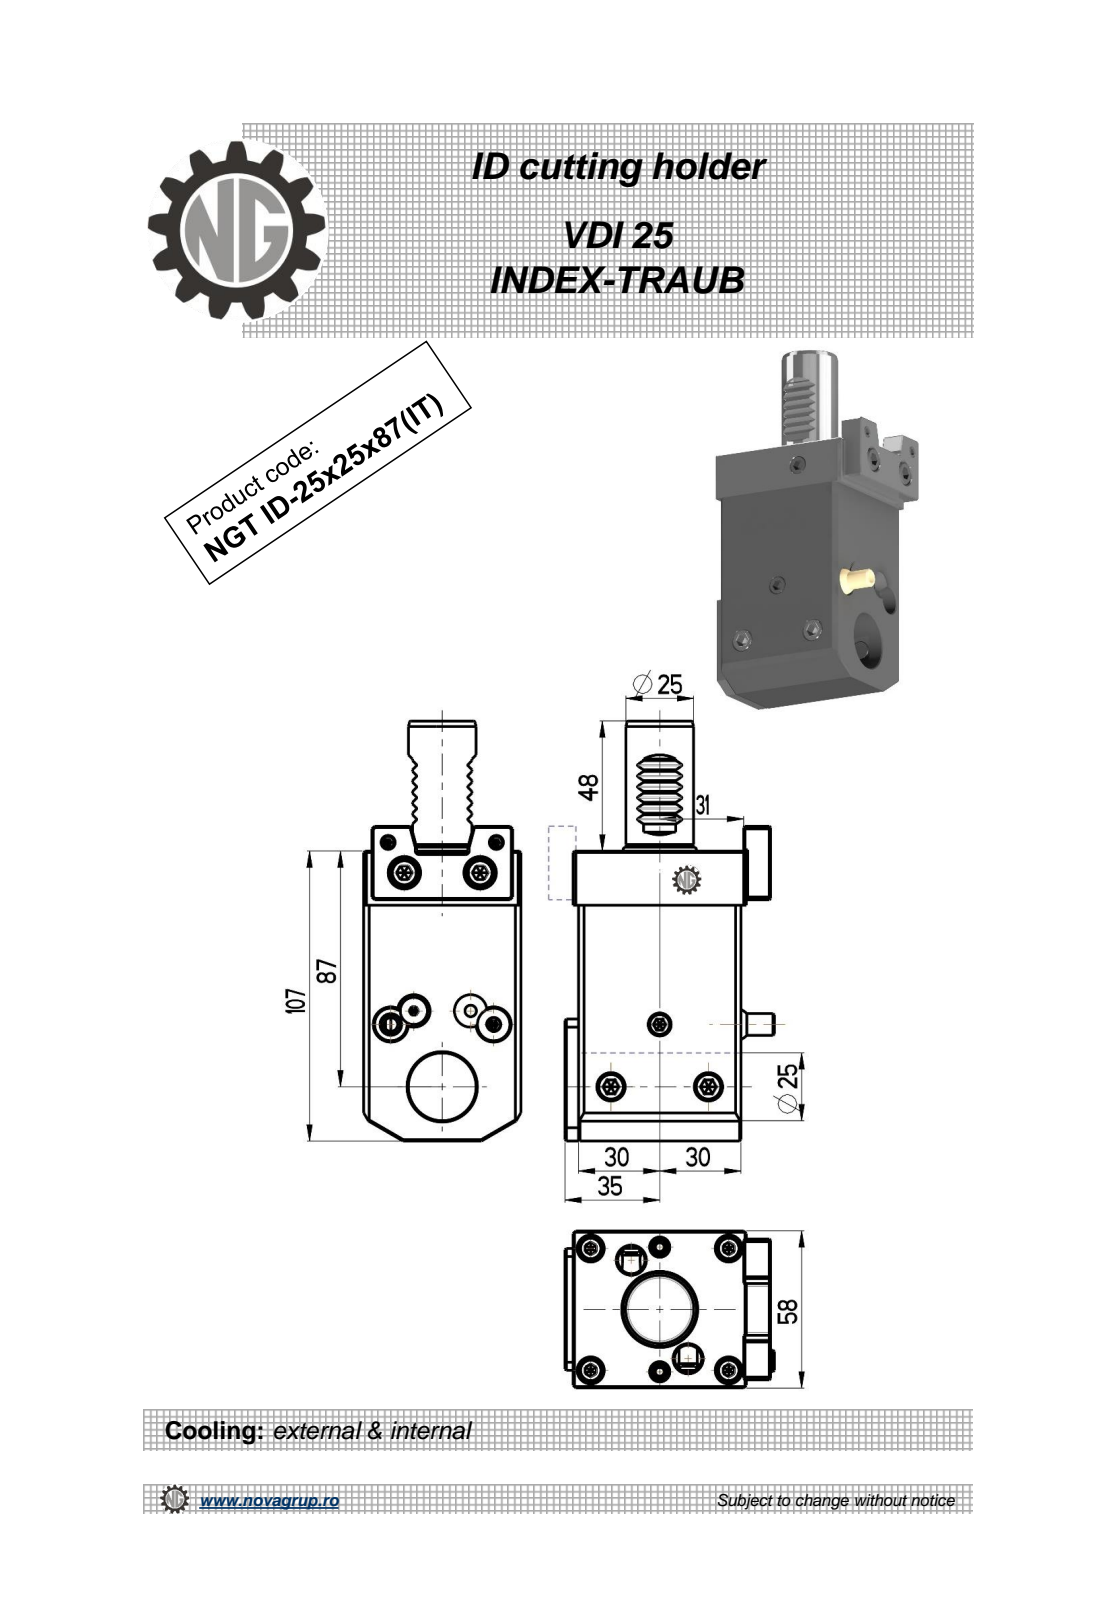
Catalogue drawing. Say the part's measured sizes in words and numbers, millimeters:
The part is named "NGT_ID_25_25_87_IT". Its 3-D file was written by "PRO/ENGINEER BY PARAMETRIC TECHNOLOGY CORPORATION, 2010280 (CONFIG_CONTROL_DESIGN)". It is 1 solid with 547 faces: 264 planar, 139 cylindrical and 144 other. Overall it measures 155 by 77.34 by 58 millimeters. Its volume is 377 659 cubic millimeters and its surface area 47 223 square millimeters. Round holes: 4 of diameter 5, 3 of diameter 4.2, 2 of diameter 10, 2 of diameter 12, 1 of diameter 25. Round bosses or shafts: 5 of diameter 10, 1 of diameter 25, 1 of diameter 8, 1 of diameter 5. Partial cylindrical surfaces (rounded edges, fillets, slot ends): 26 of radius 0.2, 20 of radius 0.51, 12 of radius 0.3, 10 of radius 0.26, 6 of radius 0.31, 2 of radius 1, 2 of radius 4.25, 2 of radius 8. The main face-to-face distances are 58, 60, 107, 2, 3, 65, 5, 62, 11, 71. The hole center spacings are 12.71, 29.83, 35.8, 56.22, 65, 67.21, 77.7, 80.23.
